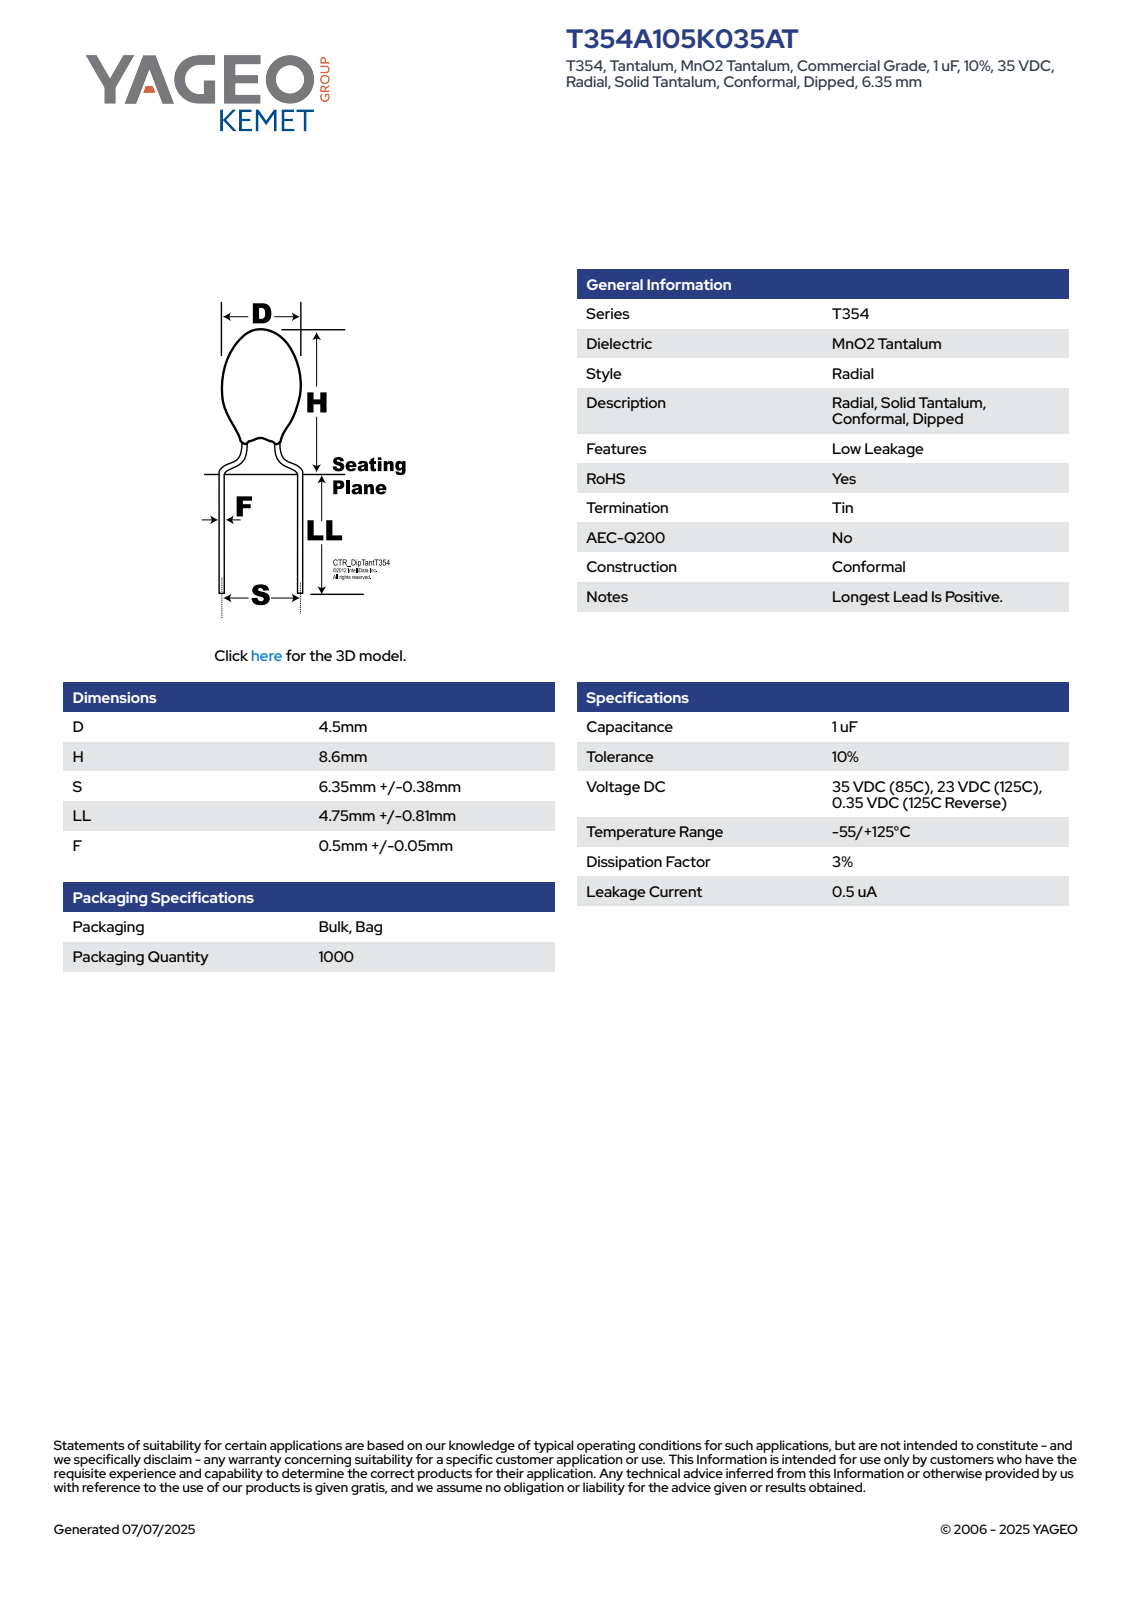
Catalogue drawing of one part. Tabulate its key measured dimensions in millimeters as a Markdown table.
| quantity | value |
| --- | --- |
| part name | CTR_T354_D4.5H8.6S6.35LL5.56F0.55 |
| STEP written by | SolidWorks 2014 (AUTOMOTIVE_DESIGN) |
| units | millimeters |
| bodies | 1 solid, 81 faces (26 planar, 10 cylindrical, 45 other) |
| overall size | 14.16 × 6.9 × 4.5 |
| volume | 91 mm³ |
| surface area | 134 mm² |
| round bosses / shafts (diameter × count) | 0.55 × 2, 4.5 × 1 |
| partial cylindrical surfaces (radius × count) | 2.24 × 1 |
| main face-to-face distances | 6, 8.16, 14.16, 12.24, 4.08, 1.92, 11.44, 3.28, 0.8, 2.72 |
